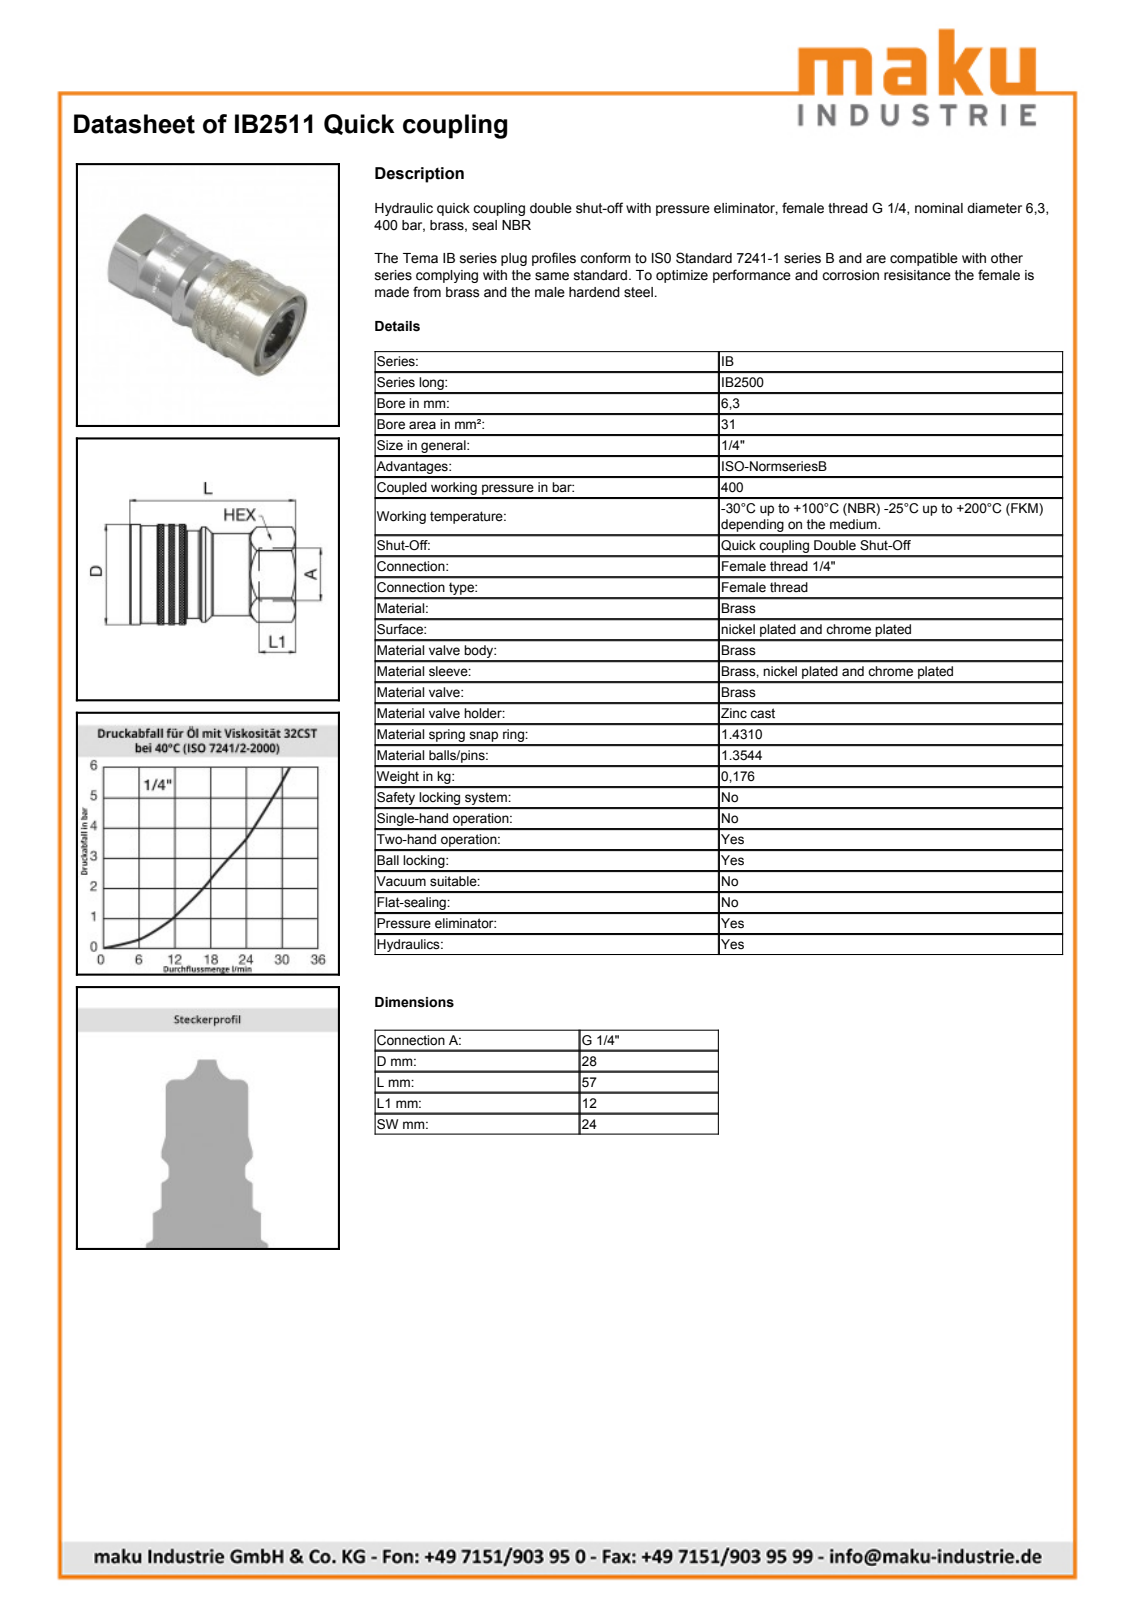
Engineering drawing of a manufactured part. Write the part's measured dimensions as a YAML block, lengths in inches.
part_name: "IB2511"
step_written_by: "SolidWorks 2009 (AUTOMOTIVE_DESIGN)"
units: inches
bodies: {solids: 2, faces: 263, planar: 40, cylindrical: 83, other: 140}
overall_size: [2.244, 1.102, 1.102]
volume: 1.451
surface_area: 14.38
round_holes:
  - {diameter: 0.039, count: 2}
  - {diameter: 0.067, count: 1}
  - {diameter: 0.094, count: 1}
  - {diameter: 0.315, count: 1}
  - {diameter: 0.45, count: 1}
  - {diameter: 0.563, count: 1}
  - {diameter: 0.567, count: 1}
  - {diameter: 0.622, count: 1}
  - {diameter: 0.622, count: 1}
  - {diameter: 0.839, count: 1}
  - {diameter: 0.957, count: 1}
  - {diameter: 1.012, count: 1}
round_bosses_or_shafts:
  - {diameter: 1.102, count: 1}
  - {diameter: 1.055, count: 1}
  - {diameter: 1.051, count: 1}
  - {diameter: 0.929, count: 1}
  - {diameter: 0.835, count: 1}
  - {diameter: 0.776, count: 1}
  - {diameter: 0.059, count: 1}
partial_cylinders:
  - {radius: 0.348, count: 1}
  - {radius: 0.476, count: 1}
  - {radius: 0.524, count: 1}
face_to_face_distances: [0.945, 0.079, 0.169, 0.442, 1.352, 0.91, 2.244, 1.802, 0.892, 1.378]
